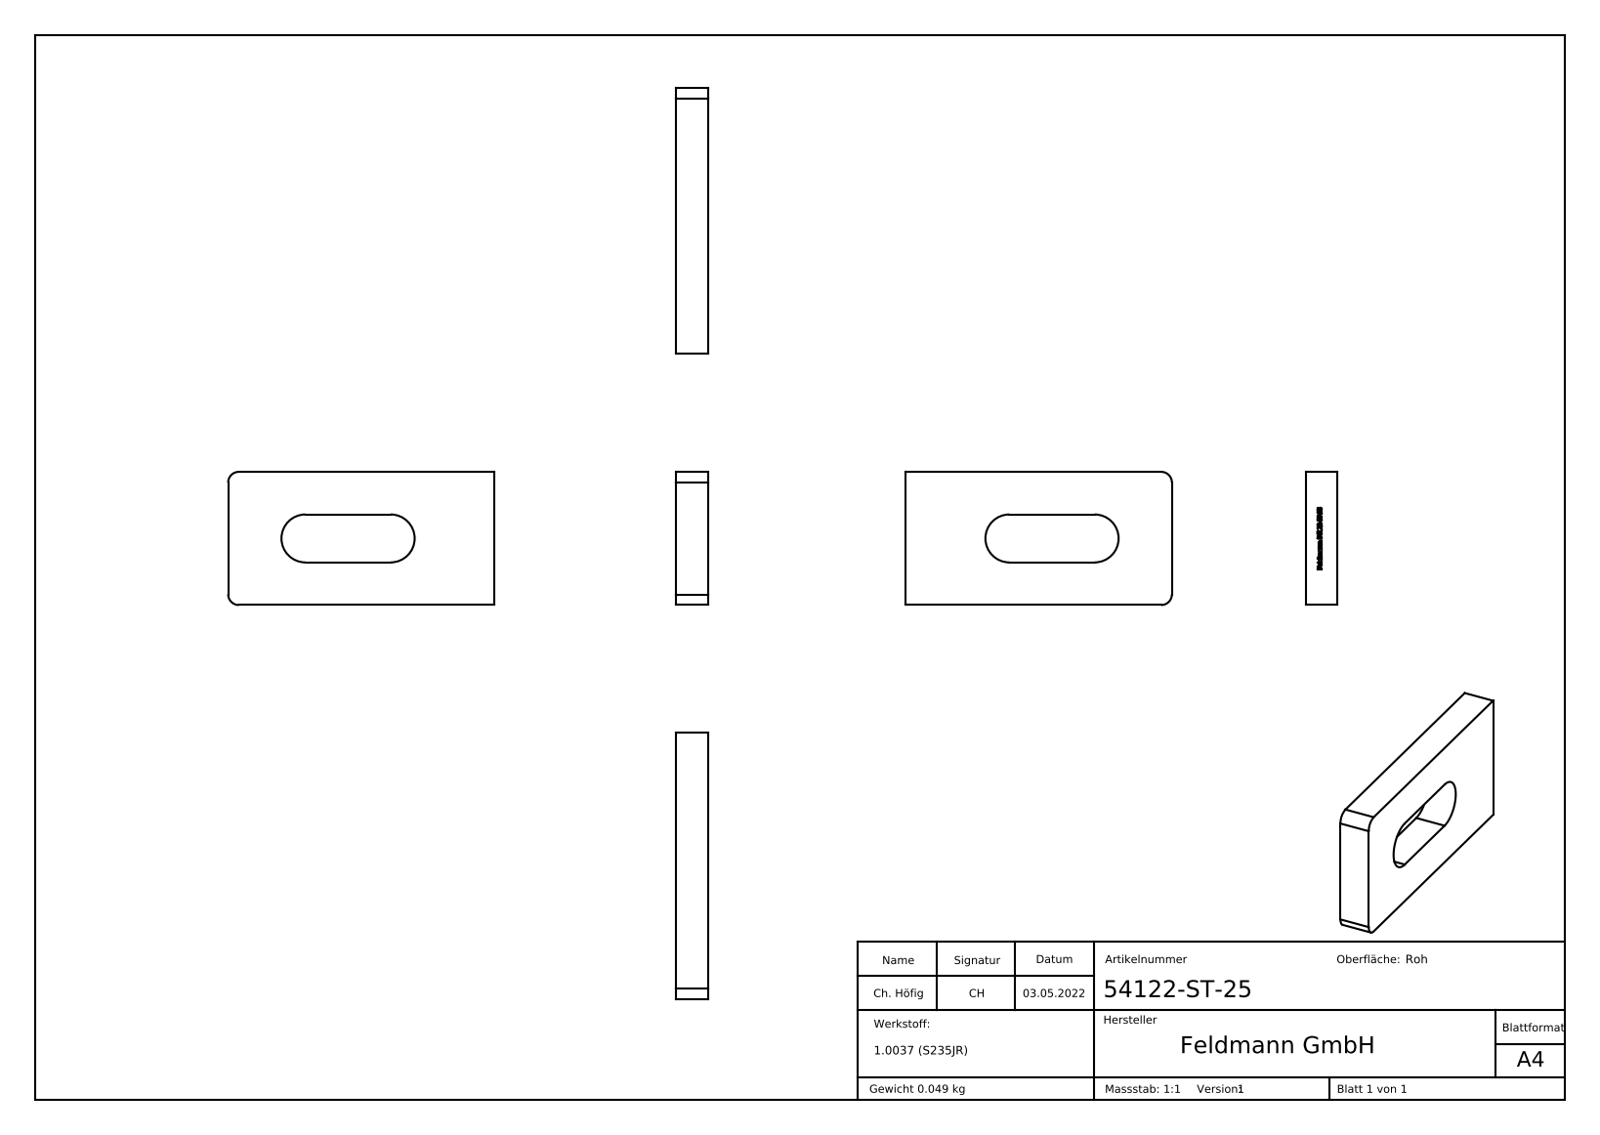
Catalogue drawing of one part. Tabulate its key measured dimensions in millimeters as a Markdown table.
| quantity | value |
| --- | --- |
| part name | 54122-ST-25 |
| STEP written by | SolidWorks 2018 (CONFIG_CONTROL_DESIGN) |
| units | millimeters |
| bodies | 1 solid, 253 faces (152 planar, 4 cylindrical, 97 other) |
| overall size | 50 × 25 × 6 |
| volume | 6 244 mm³ |
| surface area | 3 339 mm² |
| partial cylindrical surfaces (radius × count) | 2 × 2, 4.5 × 2 |
| main face-to-face distances | 6, 25, 8, 17, 50, 9, 49.9, 3, 2.65, 0.71 |
